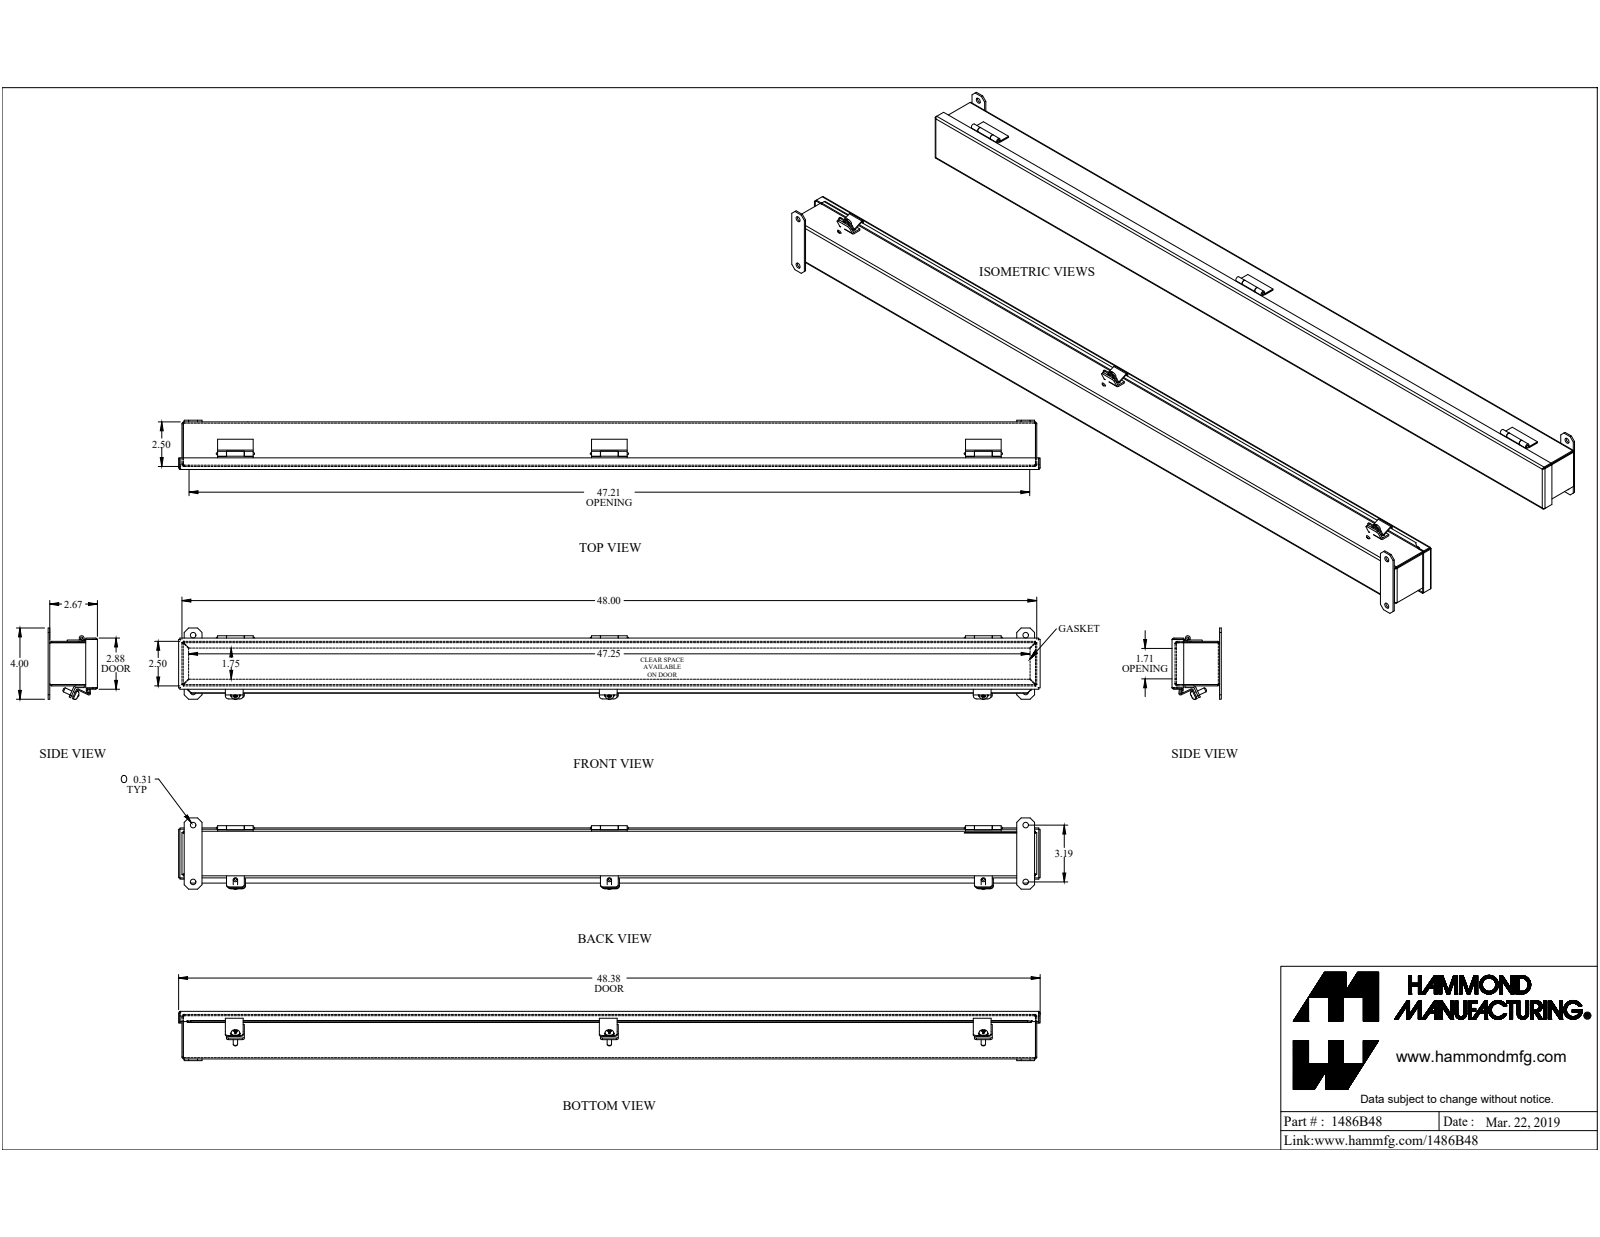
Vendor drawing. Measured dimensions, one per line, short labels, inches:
name: 1486B48
written by: SolidWorks 2019 (CONFIG_CONTROL_DESIGN)
unit: in
bodies: 26 solids, 536 faces (355 planar, 124 cylindrical, 57 other)
size: 48.375 × 4.006 × 2.767
volume: 54.29 in³; area: 1 403 in²
holes: 4× ⌀0.313, 3× ⌀0.213, 1× ⌀0.125
bosses: 3× ⌀0.48, 3× ⌀0.246, 1× ⌀0.275, 1× ⌀0.125
rounds: 13× R0.036, 13× R0.108, 12× R0.188, 12× R0.25, 6× R0.01, 6× R0.141, 2× R0.029, 2× R0.086
face distances: 0.072, 2.428, 2.6, 2.5, 2.356, 2.672, 2.528, 2.615, 0.187, 0.187
hole spacings: 3.188, 21, 46.75, 46.859, 42
